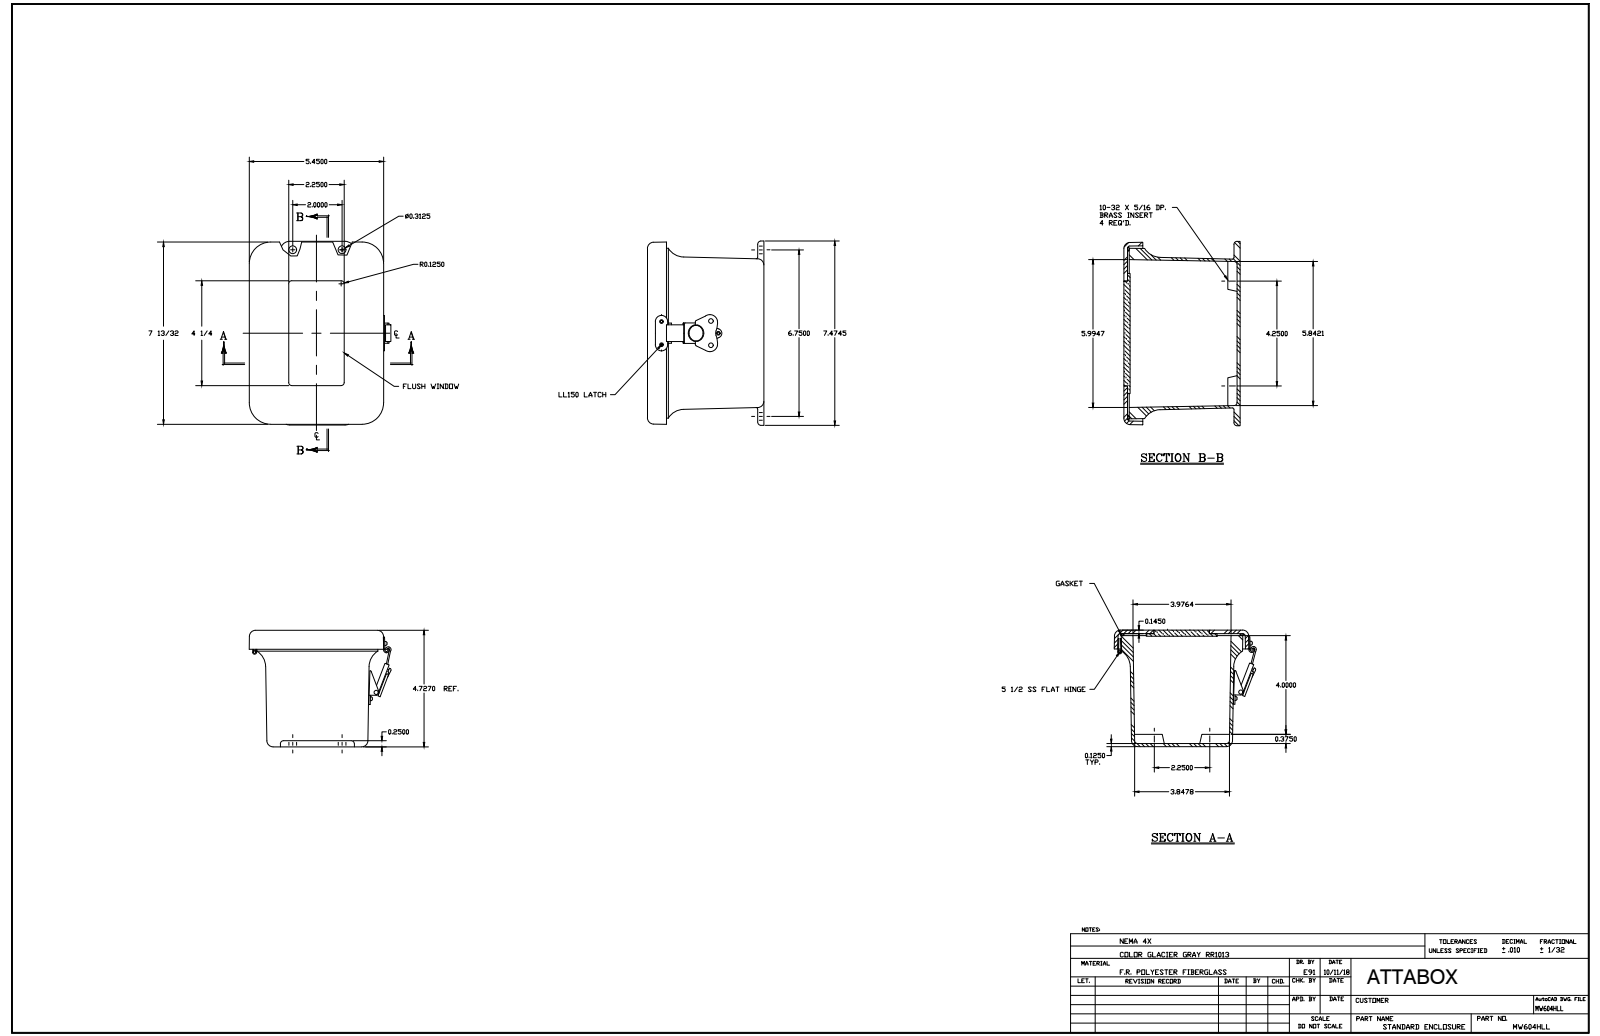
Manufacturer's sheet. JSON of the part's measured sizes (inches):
{"part_name": "MW604HLL", "step_written_by": "SolidWorks 2018 (AUTOMOTIVE_DESIGN)", "units": "inches", "bodies": {"solids": 31, "faces": 735, "planar": 307, "cylindrical": 282, "other": 146}, "overall_size": [7.474, 5.704, 4.704], "volume_in3": 33.05, "surface_area_in2": 420.6, "round_holes": [[0.14, 9], [0.131, 5], [0.152, 5], [0.156, 4], [0.218, 4], [0.13, 2], [0.165, 2], [0.197, 2], [0.085, 1], [0.085, 1], [0.106, 1], [0.118, 1]], "round_bosses_or_shafts": [[0.25, 9], [0.125, 5], [0.27, 4], [0.125, 4], [0.583, 1], [0.524, 1], [0.209, 1], [0.185, 1]], "partial_cylinders_radius": [[0.031, 20], [0.125, 16], [0.25, 12], [0.079, 10], [0.037, 4], [0.039, 4], [0.047, 4], [0.085, 4]], "face_to_face_distances": [0.145, 4.559, 4.704, 0.25, 4.454, 0.125, 4.434, 4.579, 4.329, 0.105], "hole_center_spacings": [2.5, 3.339, 0.469, 0.5, 0.7, 0.938, 1.341, 1.454]}
